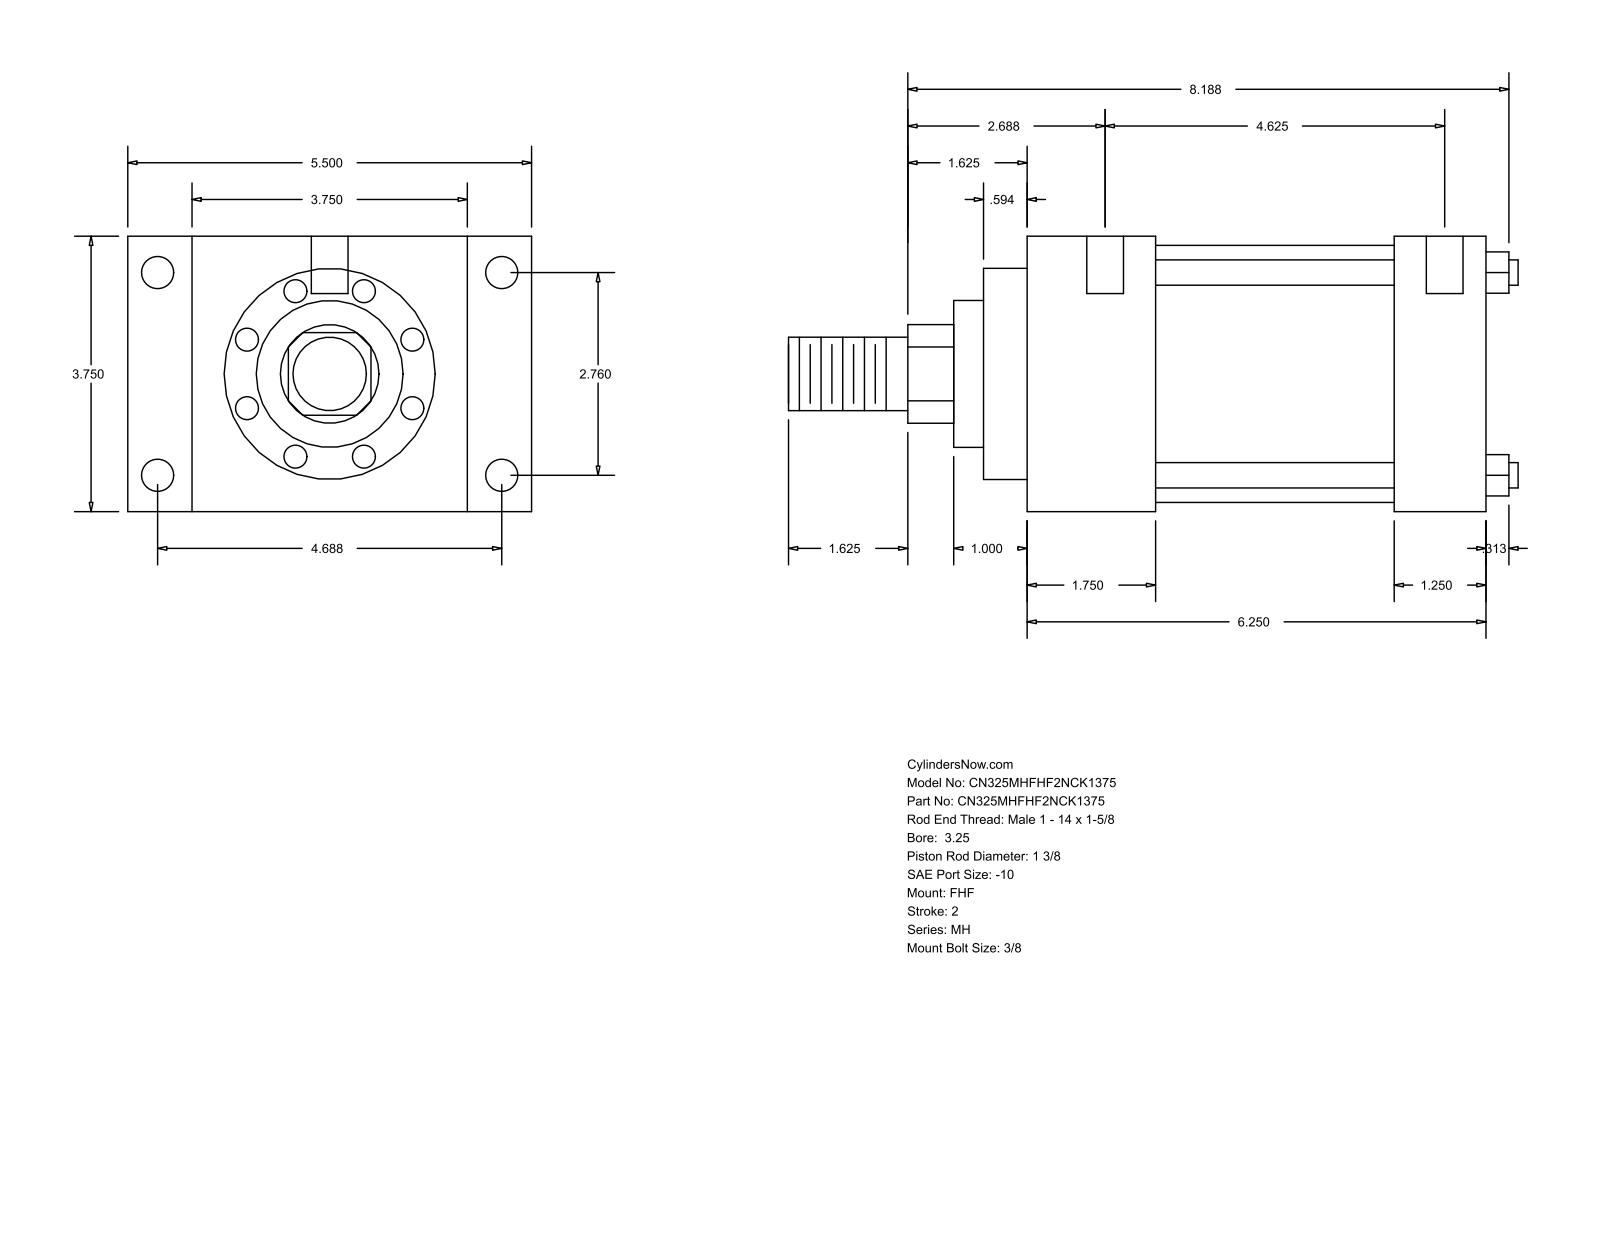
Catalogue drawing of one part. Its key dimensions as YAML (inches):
part_name: "MH_FHF__0325_1.375"
step_written_by: "GSSL Pune (CONFIG_CONTROL_DESIGN)"
units: inches
bodies: {solids: 0, faces: 90, planar: 61, cylindrical: 29, other: 0}
overall_size: [9.937, 5.5, 3.75]
round_holes:
  - {diameter: 0.219, count: 4}
  - {diameter: 0.438, count: 4}
  - {diameter: 0.5, count: 2}
round_bosses_or_shafts:
  - {diameter: 0.345, count: 4}
  - {diameter: 3.5, count: 1}
  - {diameter: 2.875, count: 1}
  - {diameter: 2, count: 1}
  - {diameter: 1.375, count: 1}
  - {diameter: 1, count: 1}
partial_cylinders:
  - {radius: 0.672, count: 1}
face_to_face_distances: [3.75, 6.25, 1.75, 4.5, 0.875, 4.625, 5.5, 5, 3.25, 1.25]
hole_center_spacings: [2.76, 4.687, 4.875, 5.439, 0.063, 0.187, 4.625, 4.688]
